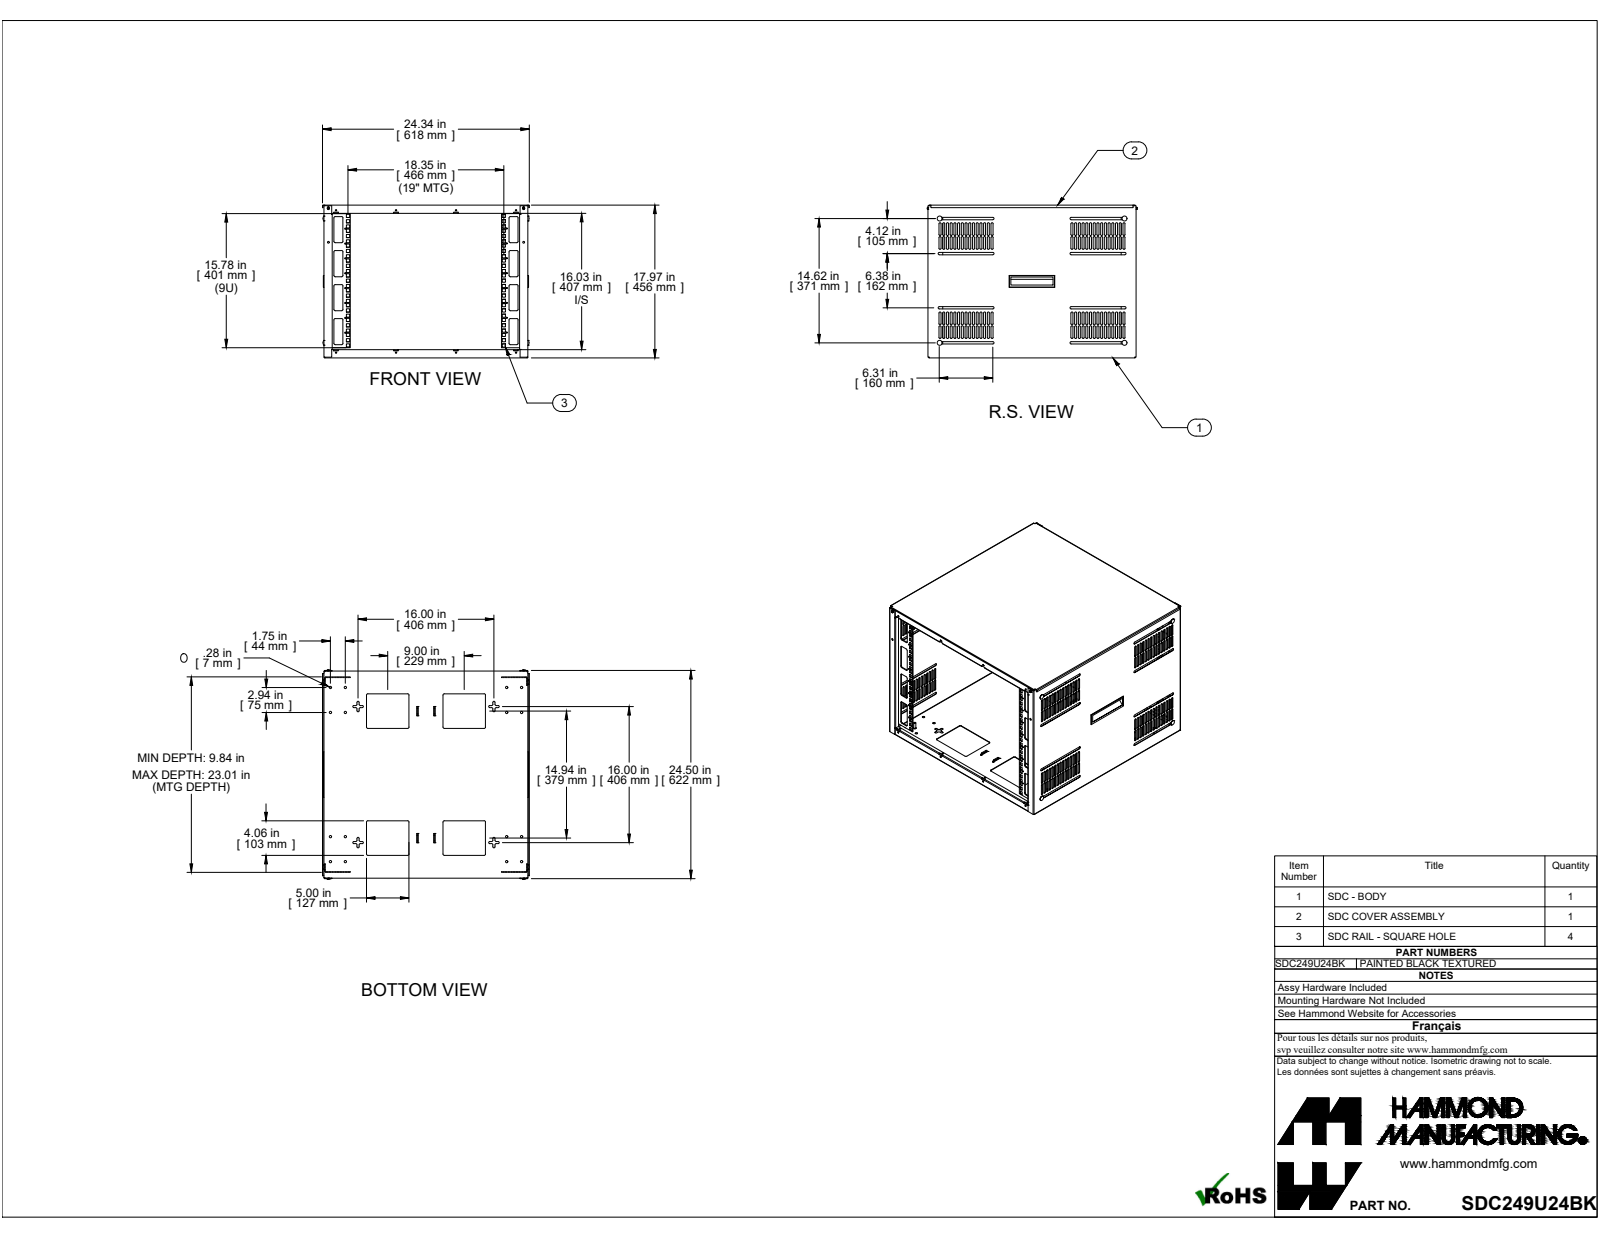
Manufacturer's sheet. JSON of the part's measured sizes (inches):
{"part_name": "SDC249U24BK", "step_written_by": "SolidWorks 2019 (CONFIG_CONTROL_DESIGN)", "units": "inches", "bodies": {"solids": 36, "faces": 2810, "planar": 1790, "cylindrical": 968, "other": 52}, "overall_size": [24.67, 24.344, 17.972], "volume_in3": 143.7, "surface_area_in2": 4855, "round_holes": [[0.125, 32], [0.17, 16], [0.281, 16], [0.196, 4], [0.159, 2], [0.187, 2], [0.213, 2]], "round_bosses_or_shafts": [[0.25, 8], [0.58, 4], [0.313, 2], [0.28, 2], [0.187, 2], [0.138, 2]], "partial_cylinders_radius": [[0.118, 240], [0.157, 68], [0.029, 22], [0.086, 22], [0.117, 18], [0.025, 16], [0.125, 16], [0.141, 16]], "face_to_face_distances": [0.057, 17.915, 23.943, 17.858, 17.972, 23.886, 24, 0.912, 0.095, 22.919], "hole_center_spacings": [1.75, 19.085, 3.5, 5.25, 19.005, 2.937, 3.419, 7]}
